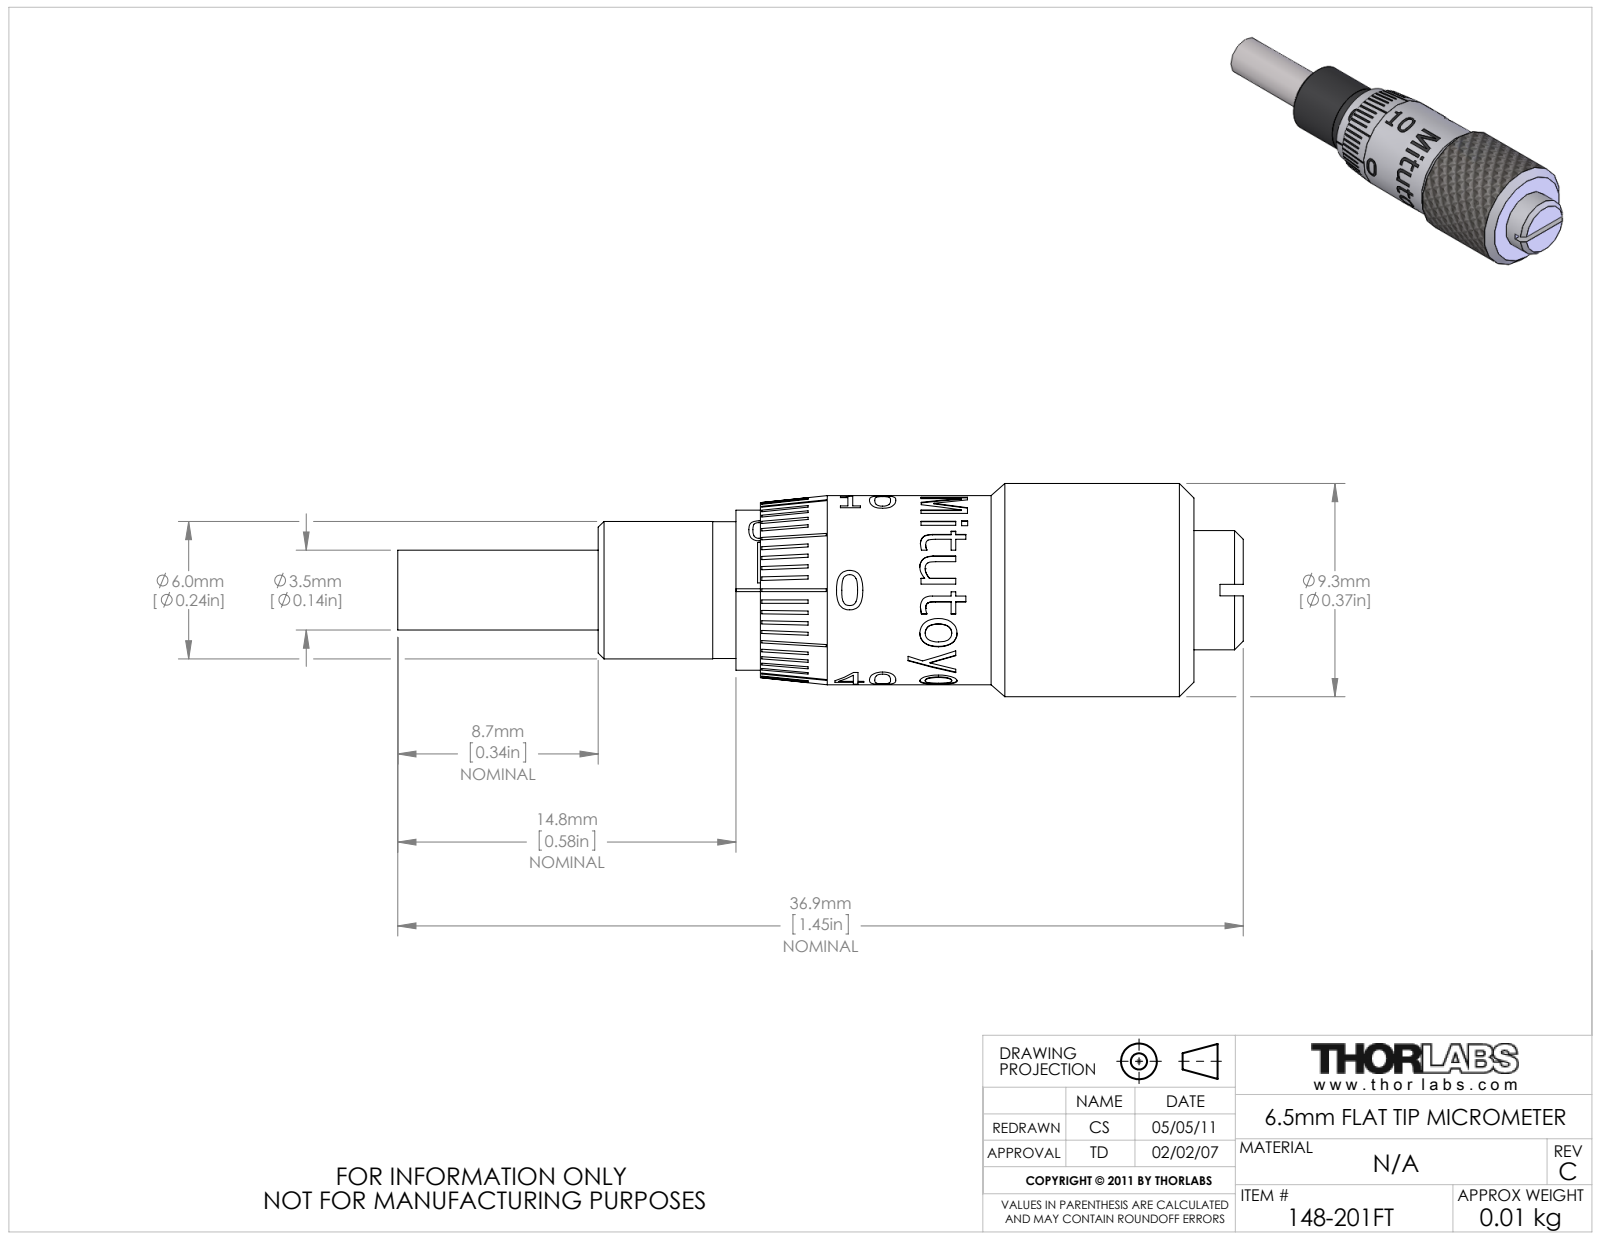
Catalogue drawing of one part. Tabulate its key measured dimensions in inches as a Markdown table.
| quantity | value |
| --- | --- |
| part name | 16383-E0W |
| STEP written by | SolidWorks 2012 (AUTOMOTIVE_DESIGN) |
| units | inches |
| bodies | 2 solids, 242 faces (68 planar, 67 cylindrical, 107 other) |
| overall size | 1.453 × 0.366 × 0.366 |
| volume | 0.102 in³ |
| surface area | 2.672 in² |
| round holes (diameter × count) | 0.138 × 1, 0.175 × 1, 0.285 × 1 |
| round bosses / shafts (diameter × count) | 0.366 × 1, 0.325 × 1, 0.275 × 1, 0.255 × 1, 0.236 × 1, 0.235 × 1, 0.205 × 1, 0.137 × 1 |
| partial cylindrical surfaces (radius × count) | 0.161 × 1 |
| main face-to-face distances | 0.565, 1.024, 0.459, 0.085, 0.65, 1.109, 0.289, 0.204, 0.361, 0.82 |
